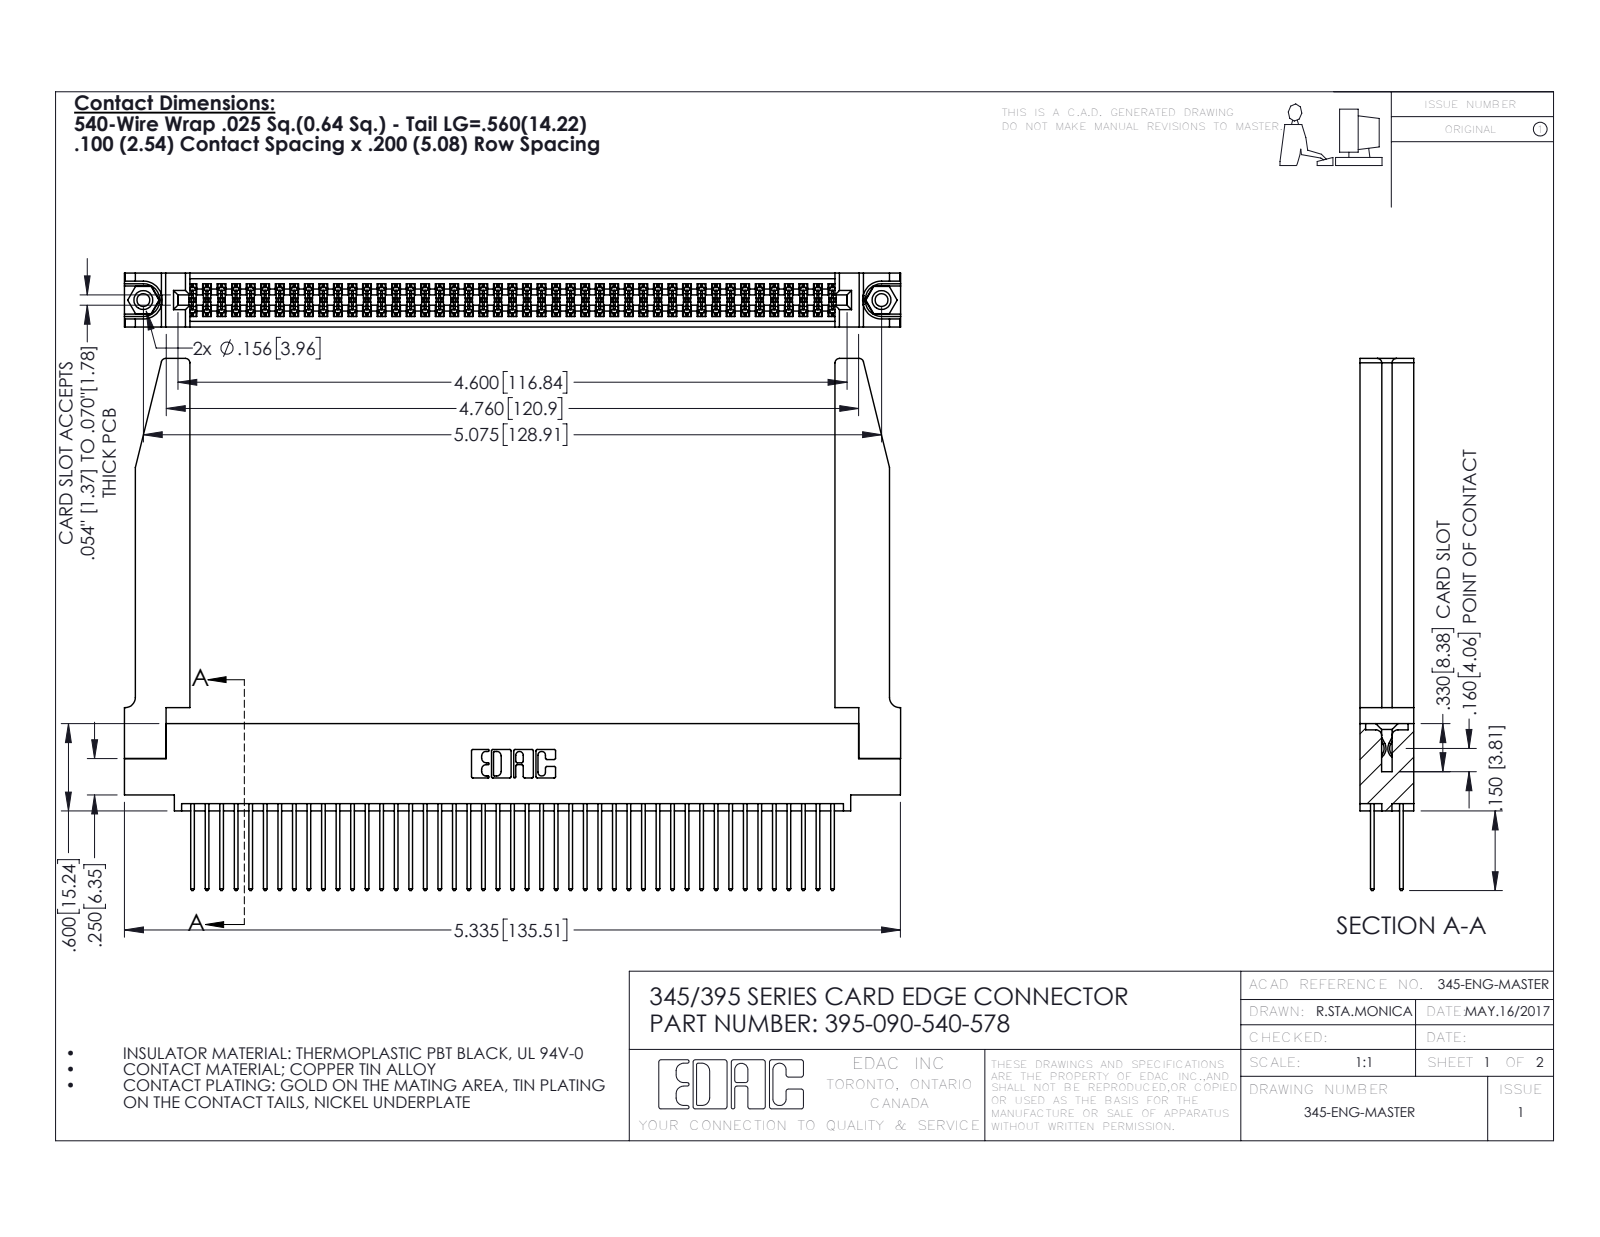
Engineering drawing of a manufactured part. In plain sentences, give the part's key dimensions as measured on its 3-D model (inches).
The part is named "345-250-001_345-250-001-102; 345-220-078_345-220-078; 345-292-001_345-293-140; 395-090-540-578 (+1 more)". Its 3-D file was written by "SolidWorks 2016 (CONFIG_CONTROL_DESIGN)". It is 95 solids with 4864 faces: 3196 planar, 1616 cylindrical and 52 other. Overall it measures 5.336 by 3.657 by 0.37 inches. Its volume is 1.296 cubic inches and its surface area 44.13 square inches. Round holes: 2 of diameter 0.089, 2 of diameter 0.125, 2 of diameter 0.156, 1 of diameter 0.064. Round bosses or shafts: 2 of diameter 0.155. Partial cylindrical surfaces (rounded edges, fillets, slot ends): 135 of radius 0.006, 90 of radius 0.01, 22 of radius 0.01, 8 of radius 0.03, 6 of radius 0.007, 6 of radius 0.031, 3 of radius 0.026, 2 of radius 0.014. The main face-to-face distances are 0.072, 0.298, 0.37, 0.2, 0.098, 0.272, 0.025, 0.225, 0.175, 0.148. The hole center spacings are 0.27, 4.839, 5.075.
